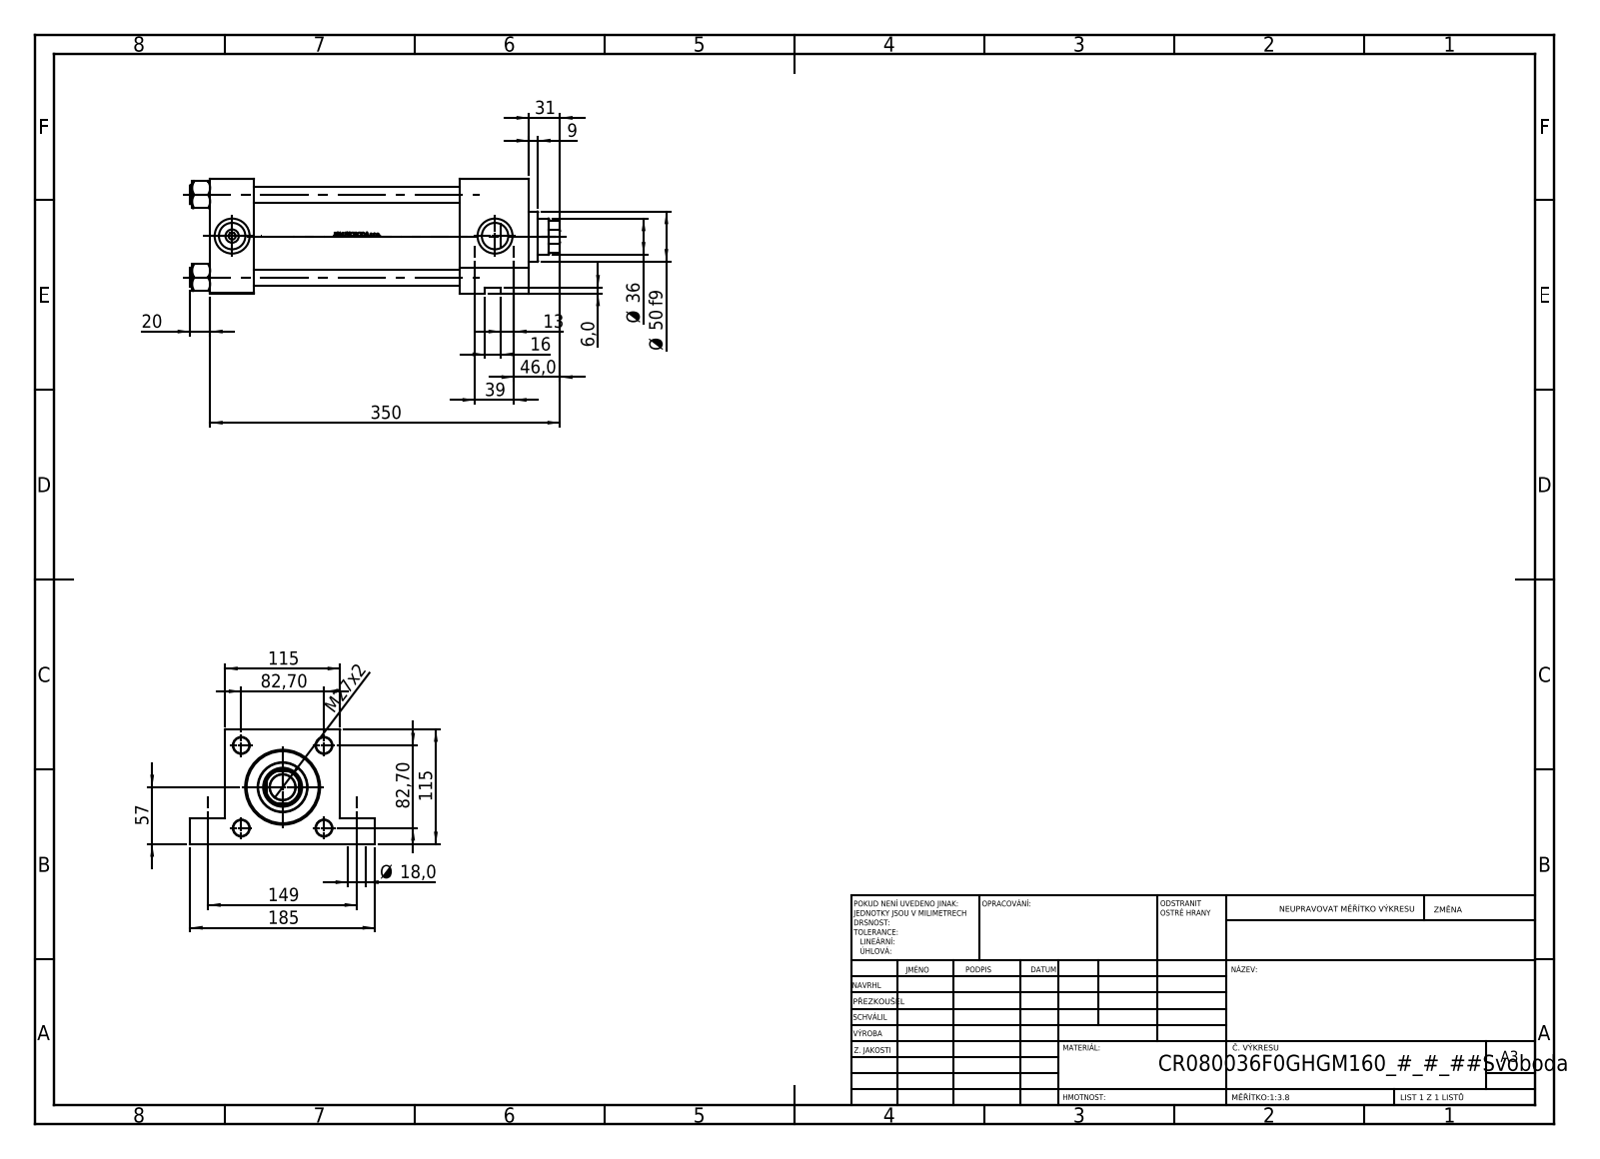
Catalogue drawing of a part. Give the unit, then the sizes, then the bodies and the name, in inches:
Units: inches
Overall size (bounding box): 14.567 × 7.283 × 4.528
Round holes (diameter × count): ⌀0.63 ×4, ⌀0.709 ×4, ⌀0.276 ×2, ⌀1.041 ×2, ⌀1.378 ×2, ⌀1.004 ×1, ⌀1.417 ×1, ⌀1.535 ×1, ⌀2.402 ×1, ⌀2.835 ×1, ⌀3.15 ×1
Round bosses / shafts (diameter × count): ⌀0.748 ×4, ⌀3.386 ×1, ⌀1.969 ×1
Partial cylindrical surfaces — rounded edges, fillets, slot ends (radius × count): R0.689 ×1
Main face-to-face distances: 4.528, 1.732, 10.827, 12.559, 9.843, 8.11, 2.717, 11.429, 9.697, 1.587
Hole centre spacings: 3.256, 1.535, 2.289, 2.316, 4.605, 5.866, 6.064, 10.354
Volume: 137.2 in³ · Surface area: 620.9 in²
Bodies: 11 solids, 1151 faces (485 planar, 126 cylindrical, 540 other)
Part name (STEP PRODUCT): V215CR_VCP_F; V215CR_F_Body; NUT_M5_F; V215_VC_A (+1 more)
STEP written by: SolidWorks 2019 (CONFIG_CONTROL_DESIGN)
